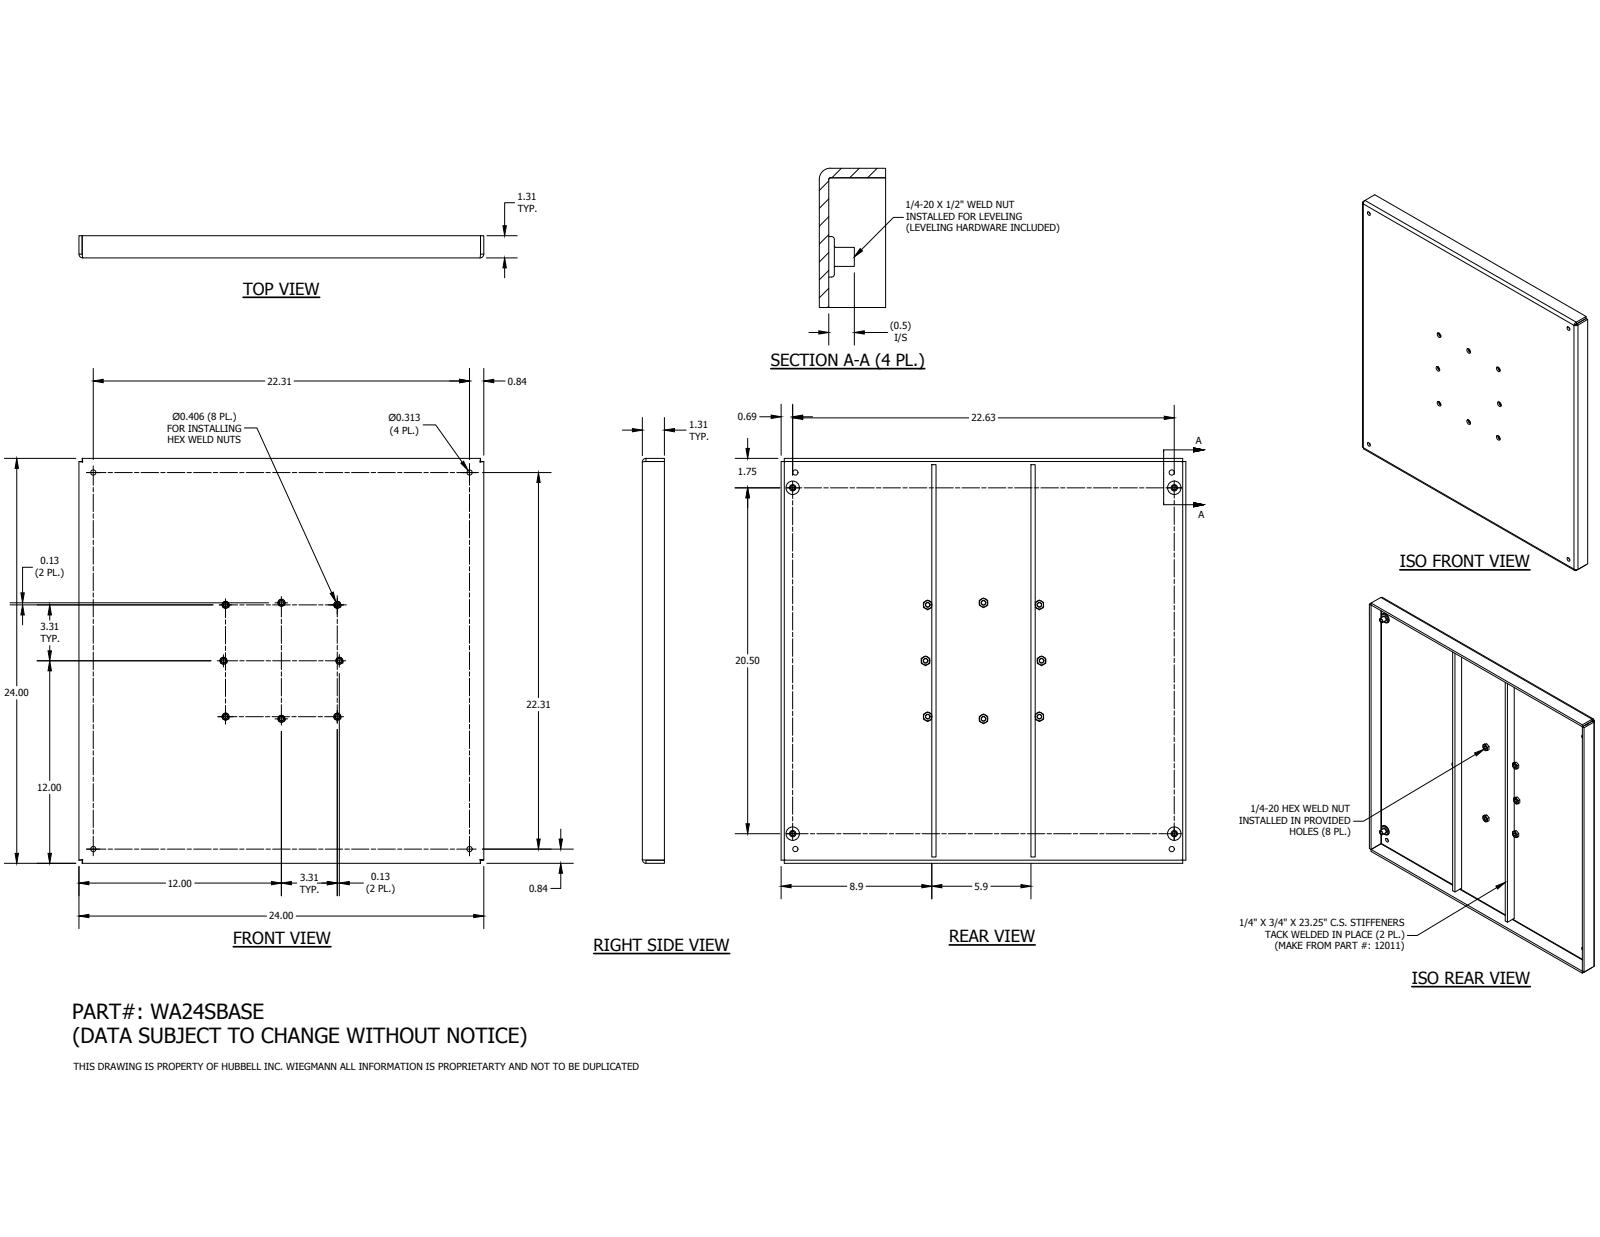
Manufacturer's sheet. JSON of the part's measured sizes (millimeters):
{"part_name": "WA24SBASEB; 34981; 34958; 12011_23.25_INCH (+1 more)", "step_written_by": "Autodesk Inventor 2016 (AUTOMOTIVE_DESIGN)", "units": "millimeters", "bodies": {"solids": 15, "faces": 314, "planar": 146, "cylindrical": 72, "other": 96}, "overall_size": [609.6, 609.6, 33.34], "volume_mm3": 2234000, "surface_area_mm2": 956406, "round_holes": [[6.35, 12], [10.32, 8], [7.94, 4]], "round_bosses_or_shafts": [[10.31, 8], [20.32, 4], [9.52, 4]], "partial_cylinders_radius": [[1.03, 21], [0.79, 4], [5.57, 4]], "face_to_face_distances": [4.78, 604.82, 609.6, 600.04, 227.01, 382.59, 222.23, 377.81, 233.36, 376.24], "hole_center_spacings": [84.2, 190.98, 344.58, 418.04, 466.59, 23.36, 123.47, 168.28]}
